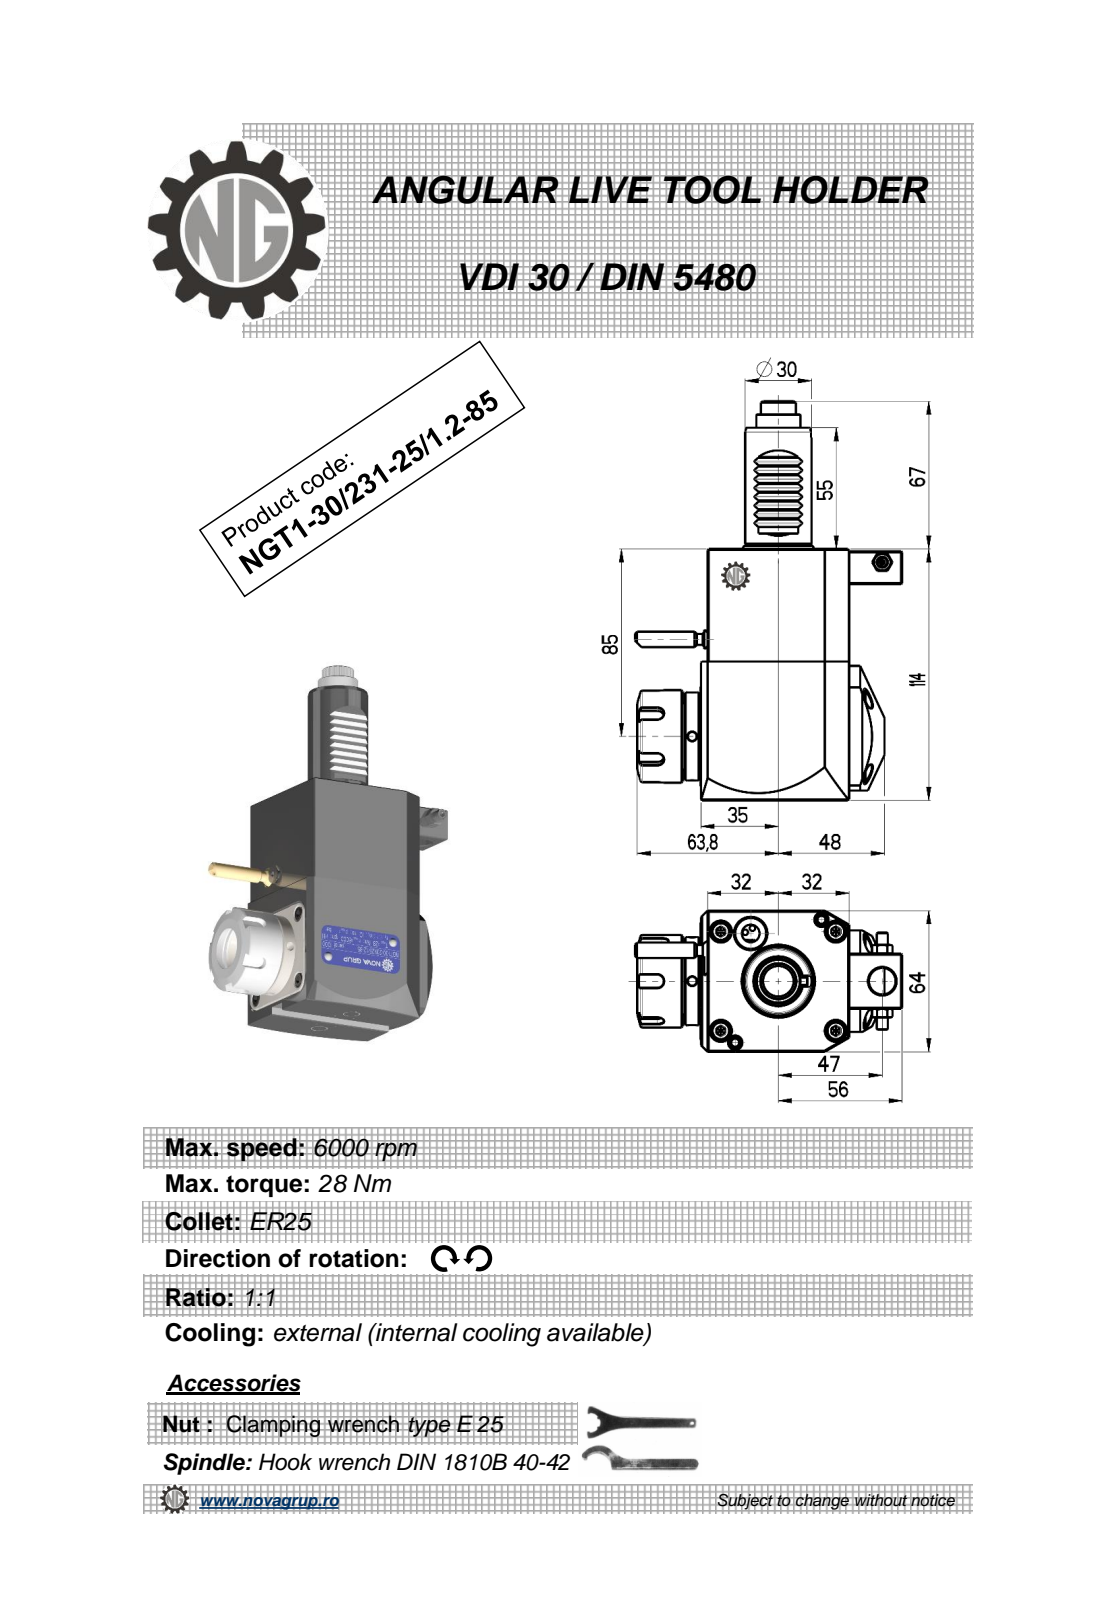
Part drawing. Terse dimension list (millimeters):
name: NGT1_30_231_25_1_2_85
written by: PRO/ENGINEER BY PARAMETRIC TECHNOLOGY CORPORATION, 2010280 (CONFIG_CONTROL_DESIGN)
unit: mm
bodies: 1 solid, 510 faces (188 planar, 161 cylindrical, 161 other)
size: 181 × 120.88 × 65.6
volume: 576 164 mm³; area: 54 702 mm²
holes: 2× ⌀4, 1× ⌀2.5, 1× ⌀3, 1× ⌀4.2, 1× ⌀9.5, 1× ⌀12, 1× ⌀20.3
bosses: 2× ⌀8.96, 2× ⌀5, 1× ⌀42, 1× ⌀40, 1× ⌀33, 1× ⌀30, 1× ⌀20, 1× ⌀7
rounds: 36× R1.98, 12× R0.26, 8× R0.3, 5× R3, 4× R3.5, 2× R160, 1× R7.08, 1× R7.92
face distances: 64, 114, 3.2, 67.2, 67, 3, 0.5, 55, 16, 4
hole spacings: 35.39, 46.17, 76.5, 85.95, 116.74
